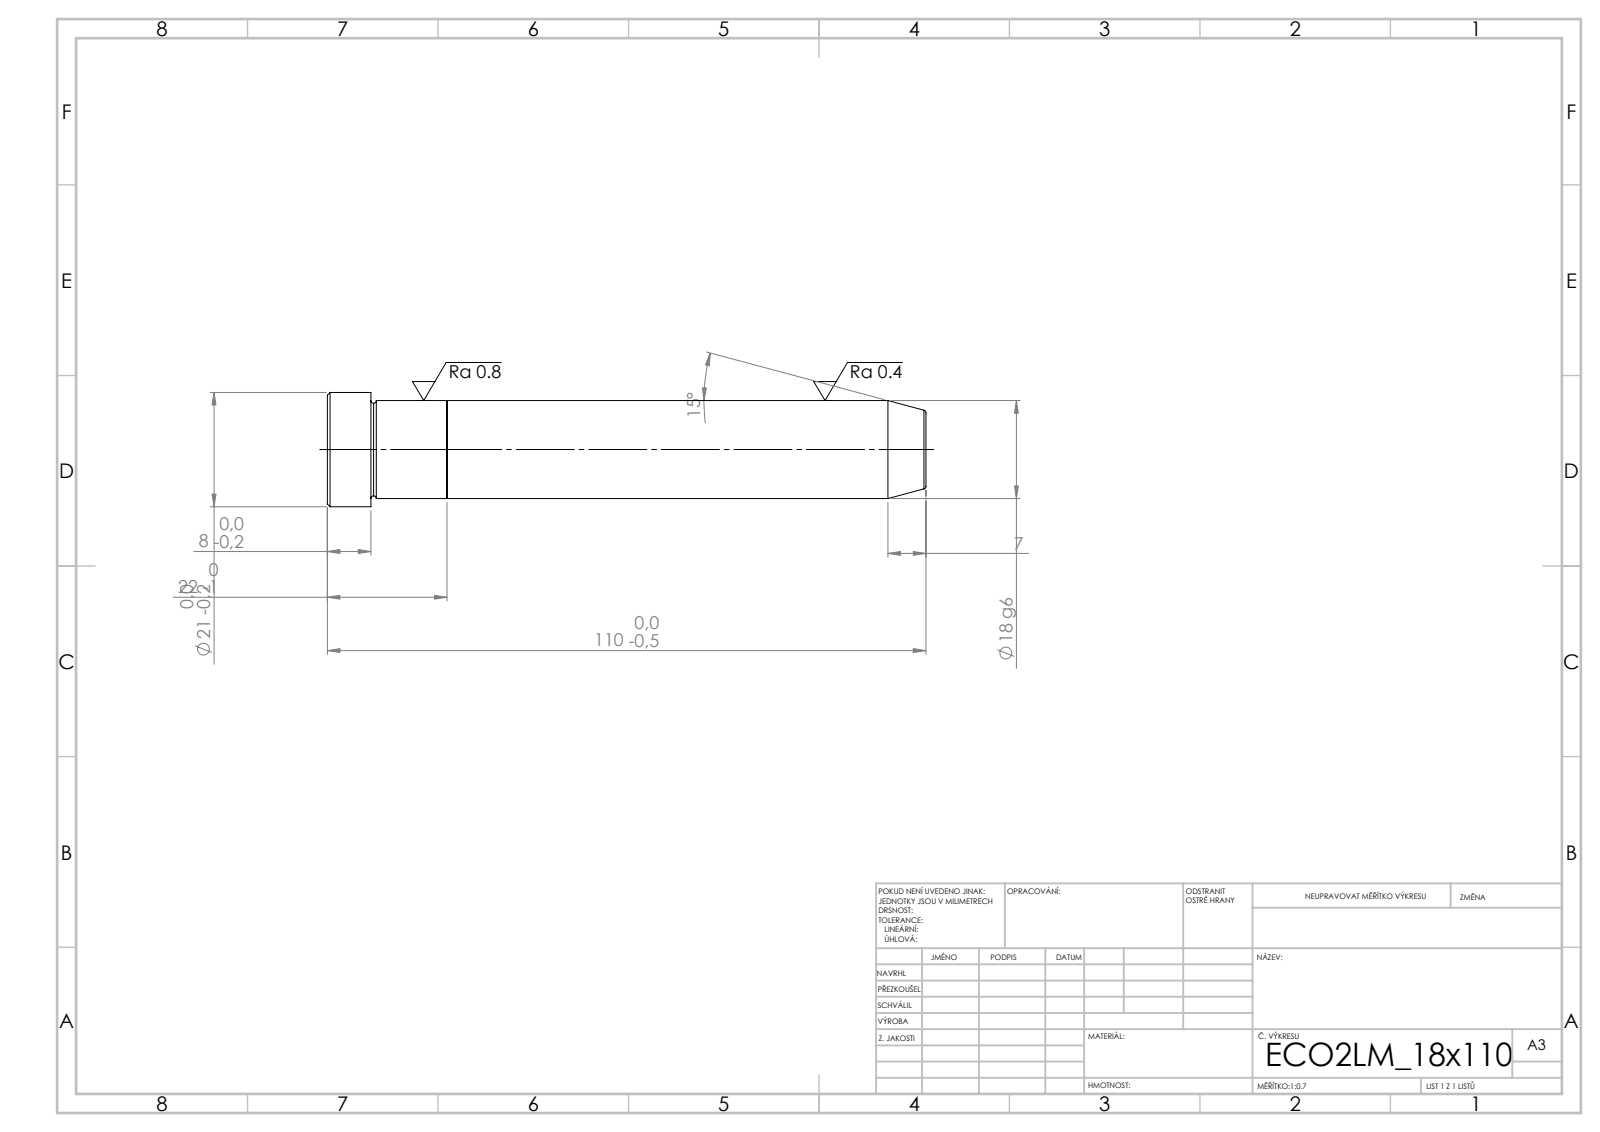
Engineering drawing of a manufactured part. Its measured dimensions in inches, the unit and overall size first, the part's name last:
Units: inches
Overall size (bounding box): 4.331 × 0.827 × 0.827
Round bosses / shafts (diameter × count): ⌀0.827 ×1, ⌀0.709 ×1
Main face-to-face distances: 0.866, 3.465, 4.331, 4.016, 0.551, 0.315
Volume: 1.73 in³ · Surface area: 11.44 in²
Bodies: 2 solids, 21 faces (5 planar, 6 cylindrical, 10 other)
STEP written by: SolidWorks 2019 (CONFIG_CONTROL_DESIGN)
